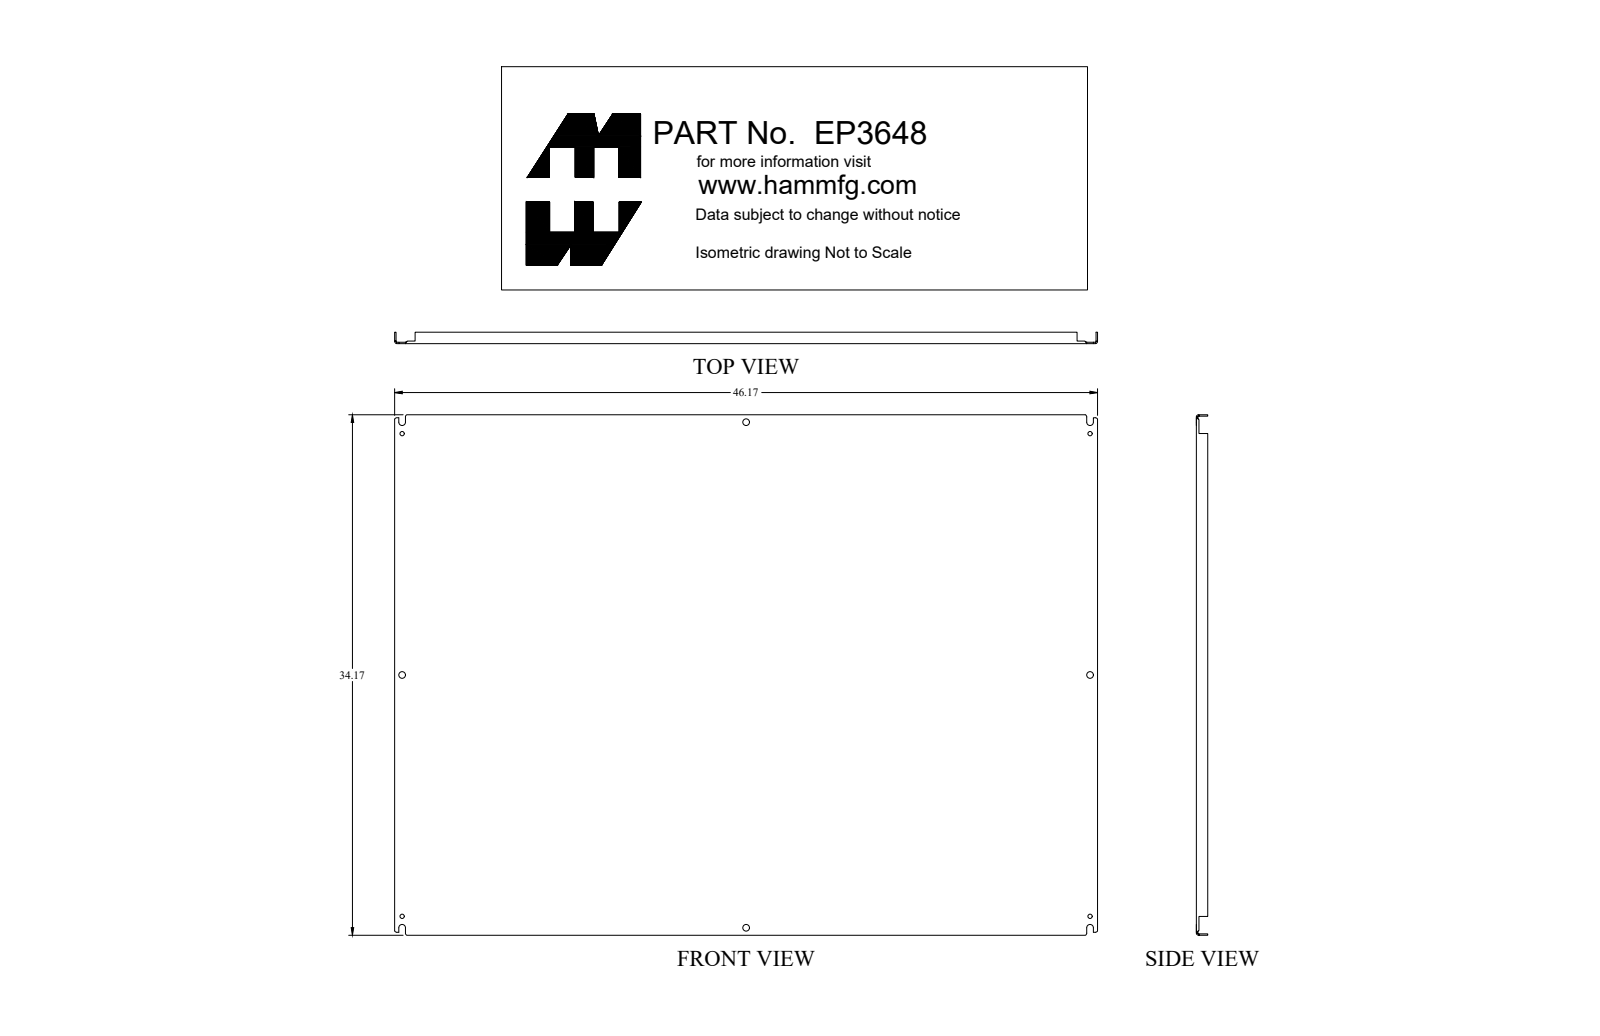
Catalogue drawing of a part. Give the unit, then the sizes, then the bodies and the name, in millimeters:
Units: millimetres
Overall size (bounding box): 1172.7 × 867.9 × 19.1
Round holes (diameter × count): ⌀7.1 ×4, ⌀11.1 ×4
Partial cylindrical surfaces — rounded edges, fillets, slot ends (radius × count): R1.2 ×4, R1.6 ×4, R3.6 ×4, R5.6 ×4
Main face-to-face distances: 2.4, 865.5, 1170.3, 867.9, 863.1, 1167.9, 1172.7, 19.1, 16.6, 4.3
Hole centre spacings: 402.4, 574.2, 712, 1004.1, 1216.3, 1147.8, 804.9, 1401.9
Volume: 2 596 000 mm³ · Surface area: 2 163 000 mm²
Bodies: 1 solid, 136 faces (74 planar, 46 cylindrical, 16 other)
Part name (STEP PRODUCT): EP3648
STEP written by: SolidWorks 2018 (AUTOMOTIVE_DESIGN)
